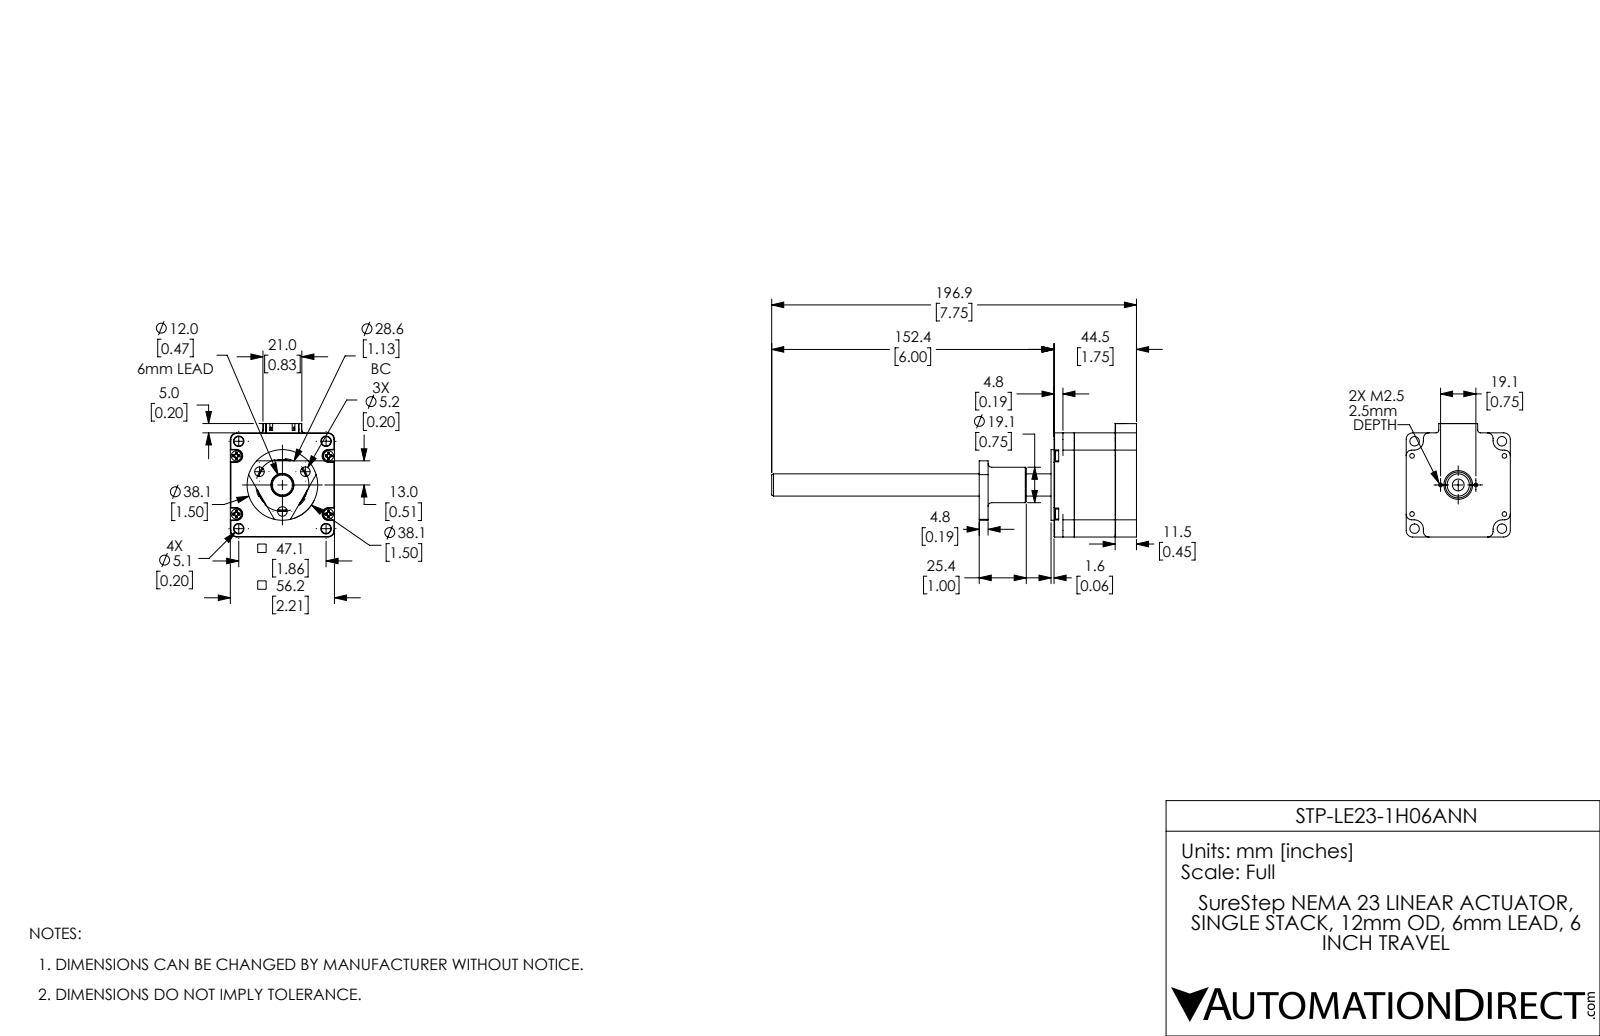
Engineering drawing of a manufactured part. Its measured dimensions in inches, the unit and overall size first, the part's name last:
Units: inches
Overall size (bounding box): 7.752 × 2.41 × 2.213
Round holes (diameter × count): ⌀0.177 ×8, ⌀0.098 ×4, ⌀0.13 ×4, ⌀0.201 ×4, ⌀0.203 ×3, ⌀0.079 ×2, ⌀0.081 ×2, ⌀0.25 ×1, ⌀0.268 ×1, ⌀0.413 ×1, ⌀0.61 ×1, ⌀0.787 ×1
Round bosses / shafts (diameter × count): ⌀0.213 ×4, ⌀1.5 ×1, ⌀1.417 ×1, ⌀1.402 ×1, ⌀1.372 ×1, ⌀0.752 ×1, ⌀0.63 ×1, ⌀0.472 ×1
Partial cylindrical surfaces — rounded edges, fillets, slot ends (radius × count): R0.059 ×10, R0.118 ×8, R0.071 ×4, R0.126 ×4, R0.138 ×4, R0.197 ×4, R0.76 ×1
Main face-to-face distances: 0.866, 1.752, 2.213, 0.453, 1.319, 0.063, 2.024, 0.433, 1.299, 1.528
Hole centre spacings: 0.556, 0.974, 1.301, 1.378, 1.801, 1.911, 2.244, 0.258
Volume: 7.577 in³ · Surface area: 77.74 in²
Bodies: 8 solids, 712 faces (282 planar, 199 cylindrical, 231 other)
Part name (STEP PRODUCT): STP-LE23-1H06ANN_2; STP-LE23-1H06ANN; STP-LE23-1H06ANN_1
STEP written by: SolidWorks 2017 (AUTOMOTIVE_DESIGN)
